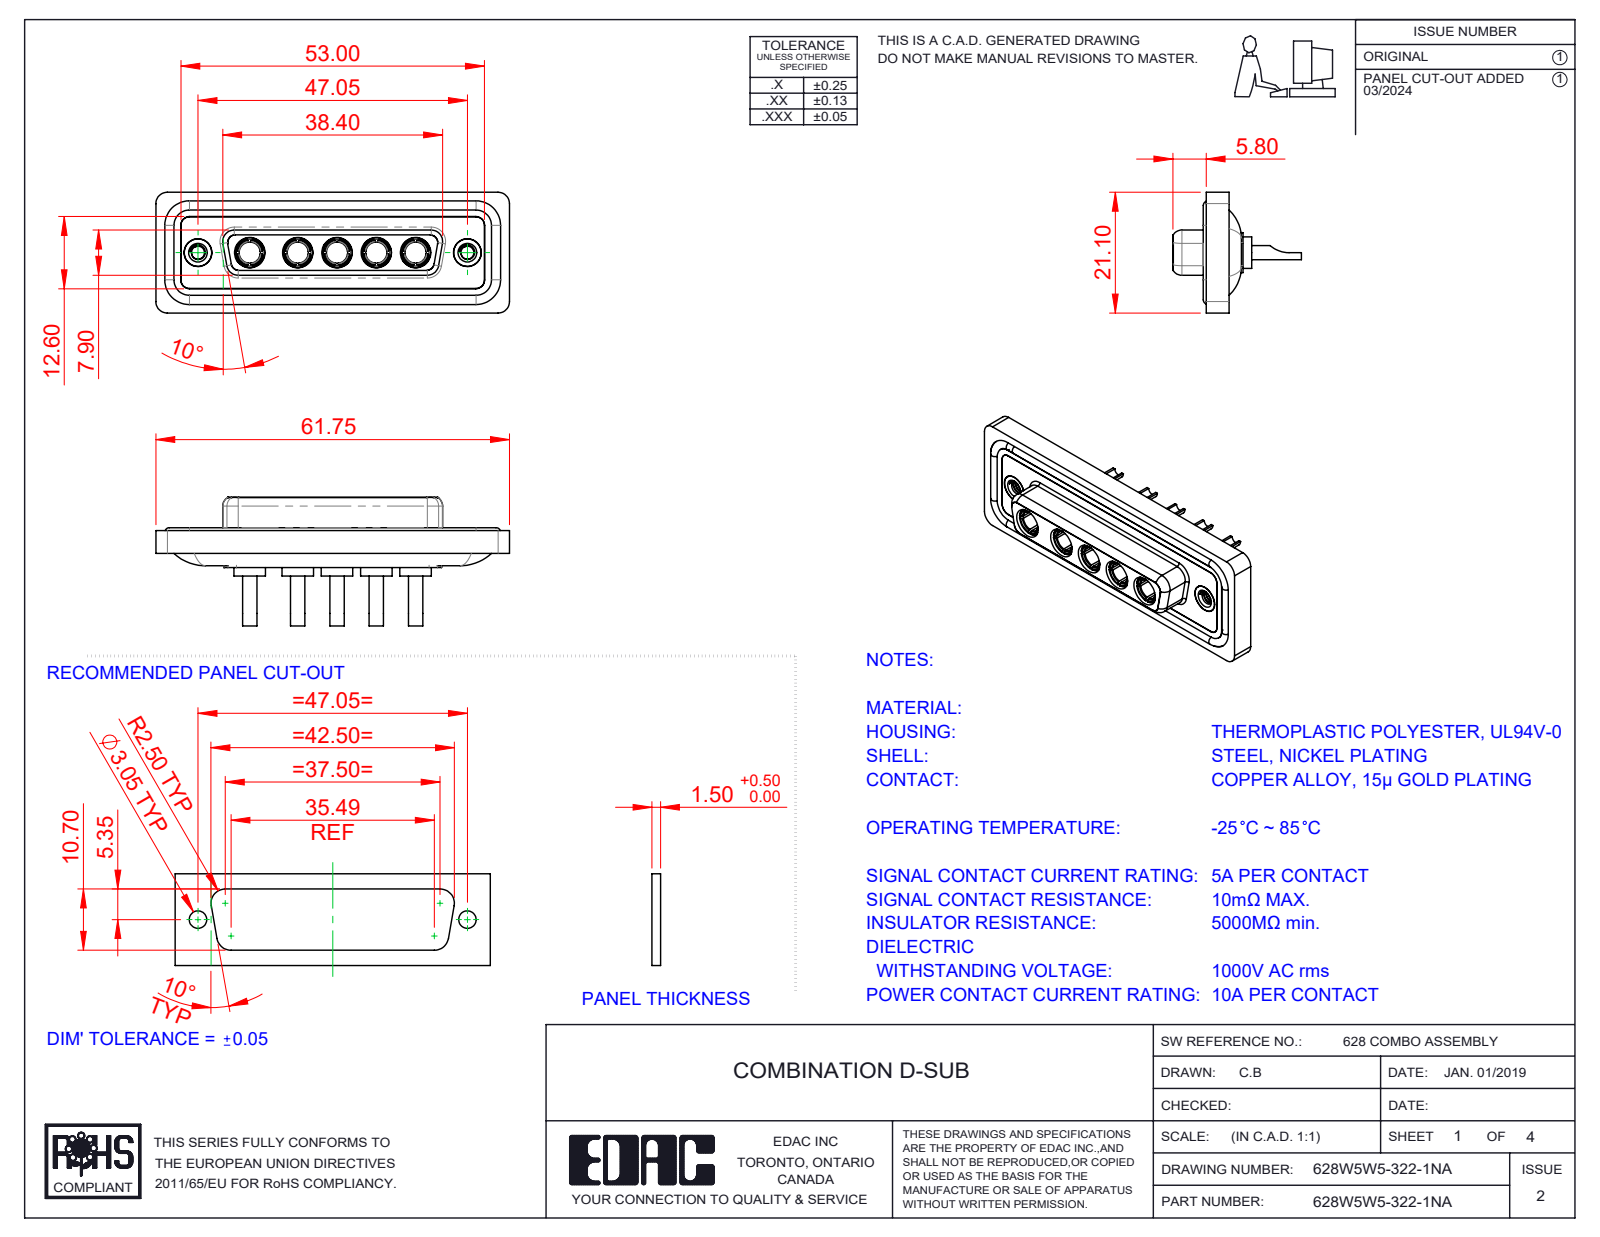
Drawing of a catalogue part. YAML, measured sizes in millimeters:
part_name: "628Combo Waterproof Housing_25 Contacts; 628Combo Shell Front_25 Contacts; 628Combo Shell Rear_25 Contacts; 628W5W5-322-1NA (+3 more)"
step_written_by: "SolidWorks 2023 (CONFIG_CONTROL_DESIGN)"
units: millimeters
bodies: {solids: 17, faces: 779, planar: 260, cylindrical: 320, other: 199}
overall_size: [61.75, 22.45, 21.1]
volume: 8160
surface_area: 13652
round_holes:
  - {diameter: 4.85, count: 7}
  - {diameter: 1.7, count: 5}
  - {diameter: 3.7, count: 5}
  - {diameter: 5.3, count: 5}
  - {diameter: 2.26, count: 2}
  - {diameter: 4, count: 2}
  - {diameter: 4.05, count: 2}
  - {diameter: 5, count: 2}
round_bosses_or_shafts:
  - {diameter: 5.5, count: 5}
  - {diameter: 5.2, count: 5}
  - {diameter: 4.96, count: 5}
  - {diameter: 4.75, count: 5}
  - {diameter: 3.75, count: 5}
  - {diameter: 2.5, count: 5}
  - {diameter: 1.6, count: 4}
  - {diameter: 4.95, count: 2}
partial_cylinders:
  - {radius: 1.5, count: 22}
  - {radius: 2, count: 18}
  - {radius: 1.35, count: 8}
  - {radius: 1.6, count: 8}
  - {radius: 2.1, count: 5}
  - {radius: 0.25, count: 4}
  - {radius: 0.5, count: 4}
  - {radius: 0.6, count: 4}
face_to_face_distances: [0.4, 1.8, 7.45, 5.65, 0.5, 7.05, 6.6, 1.6, 1.1, 2.9]
hole_center_spacings: [6.86, 9.04, 13.72, 38.01, 8.39, 15.25, 15.9, 17.43]
